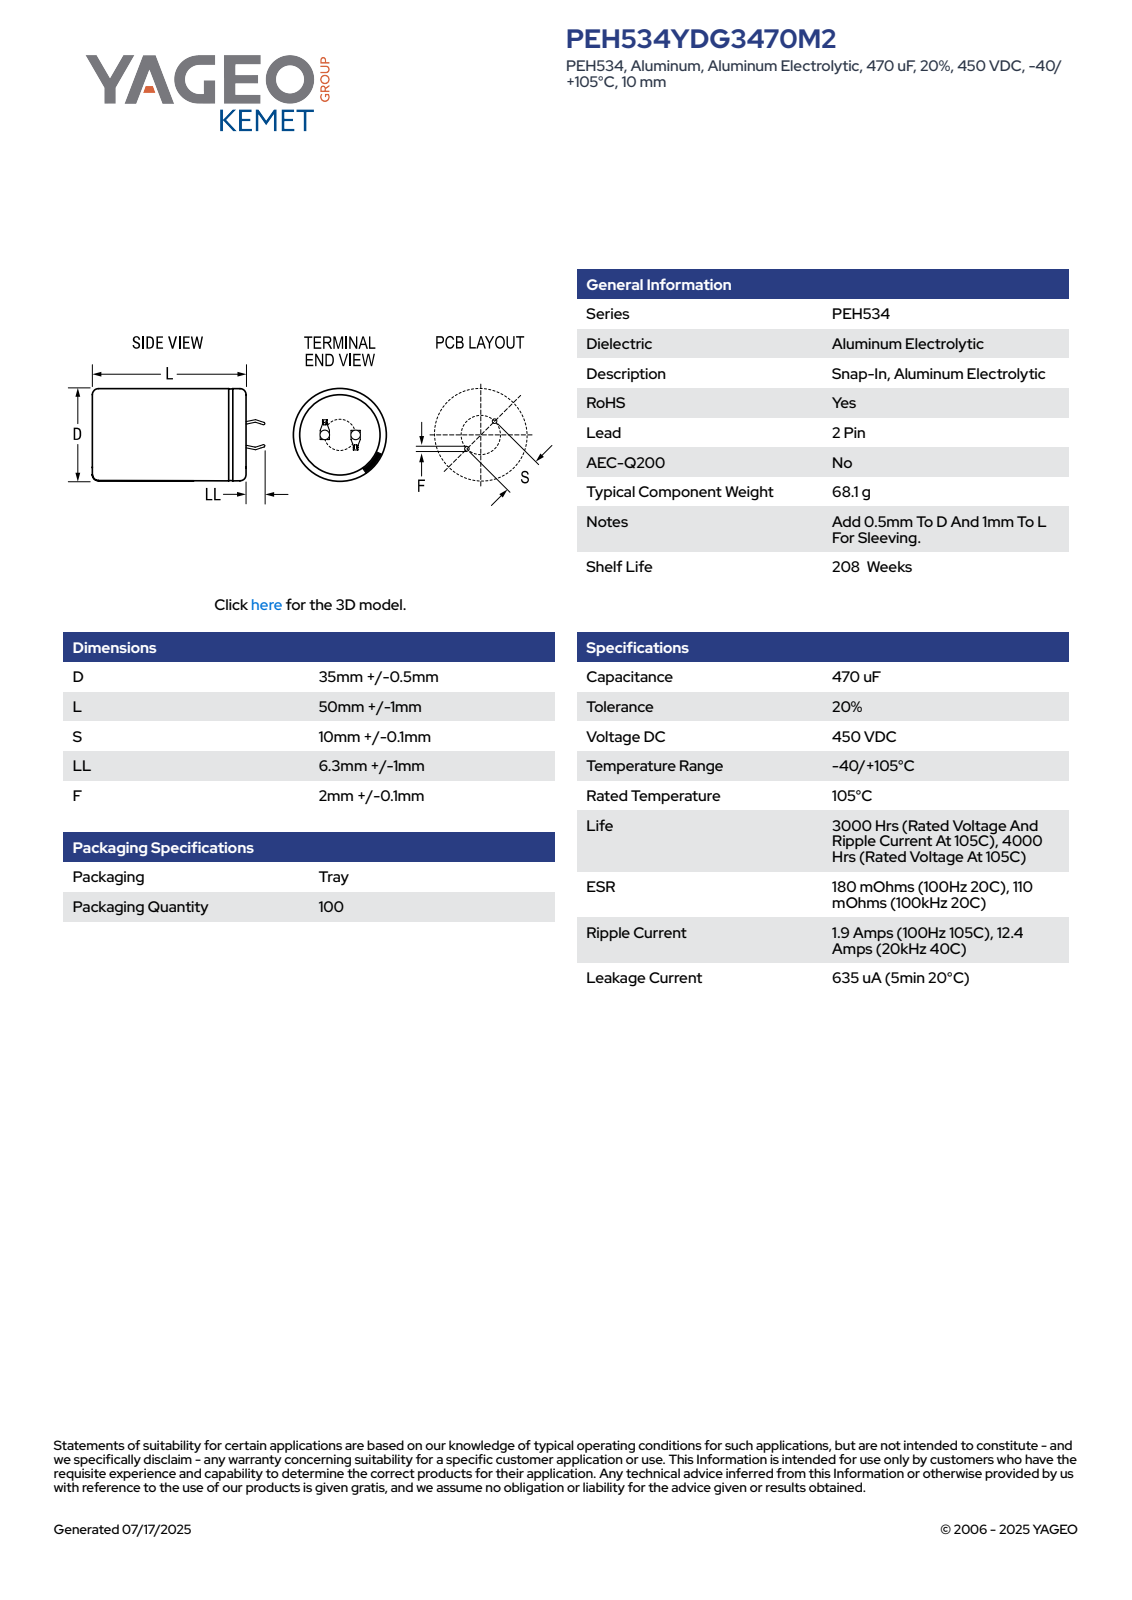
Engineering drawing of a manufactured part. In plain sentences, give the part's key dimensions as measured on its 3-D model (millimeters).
The part is named "CARS_K2P_35X50_D35.5L51S10LL7.3F2.1". Its 3-D file was written by "SolidWorks 2014 (AUTOMOTIVE_DESIGN)". It is 1 solid with 100 faces: 52 planar, 9 cylindrical and 39 other. Overall it measures 58.29 by 35.5 by 35.5 millimeters. Its volume is 49 974 cubic millimeters and its surface area 7 666 square millimeters. Round holes: 1 of diameter 31.41. Round bosses or shafts: 1 of diameter 35.5. Partial cylindrical surfaces (rounded edges, fillets, slot ends): 1 of radius 17.74. The main face-to-face distances are 50.99, 0.6, 51.49, 0.5, 7.08, 7.64, 0.75, 1.35, 7.68, 6.48.
